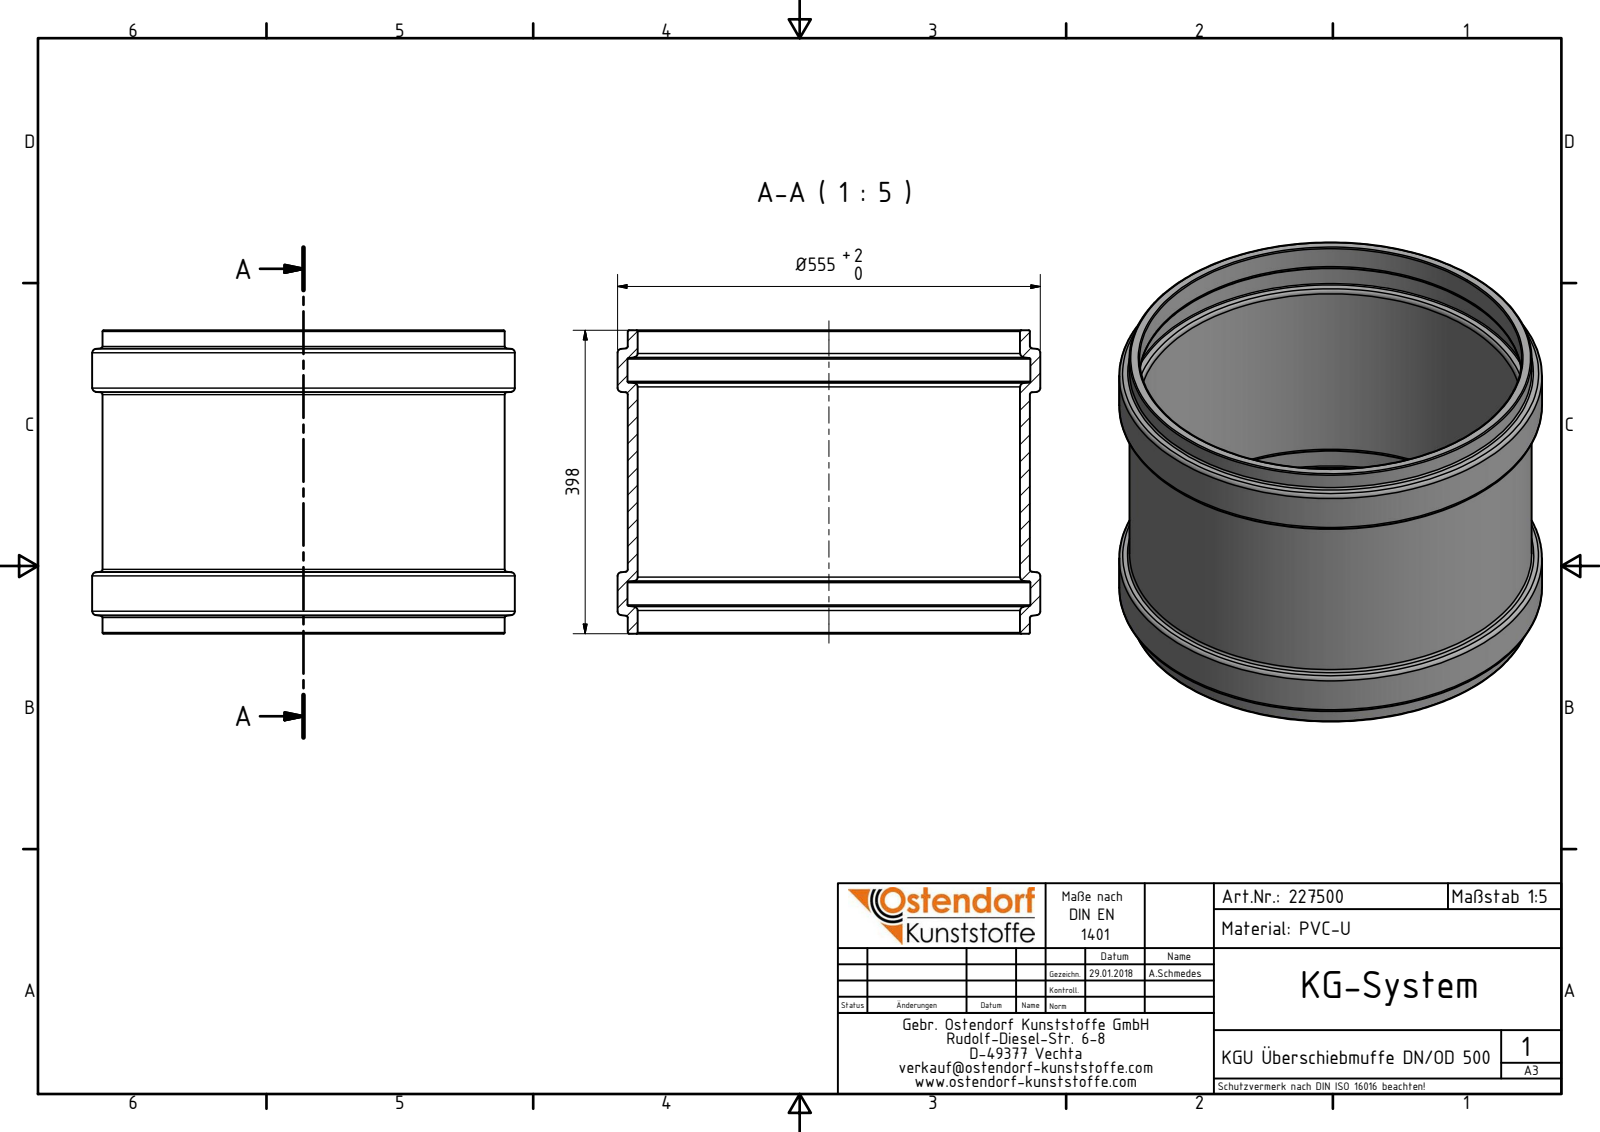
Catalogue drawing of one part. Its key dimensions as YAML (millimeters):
part_name: "227500 KGU Überschiebmuffe DN_OD 500"
step_written_by: "Autodesk Inventor 2016 (AUTOMOTIVE_DESIGN)"
units: millimeters
bodies: {solids: 1, faces: 40, planar: 2, cylindrical: 10, other: 28}
overall_size: [555, 555, 398]
volume: 9472000
surface_area: 1471000
round_holes:
  - {diameter: 502, count: 1}
  - {diameter: 529, count: 1}
round_bosses_or_shafts:
  - {diameter: 555, count: 1}
  - {diameter: 528, count: 1}
face_to_face_distances: [398]
